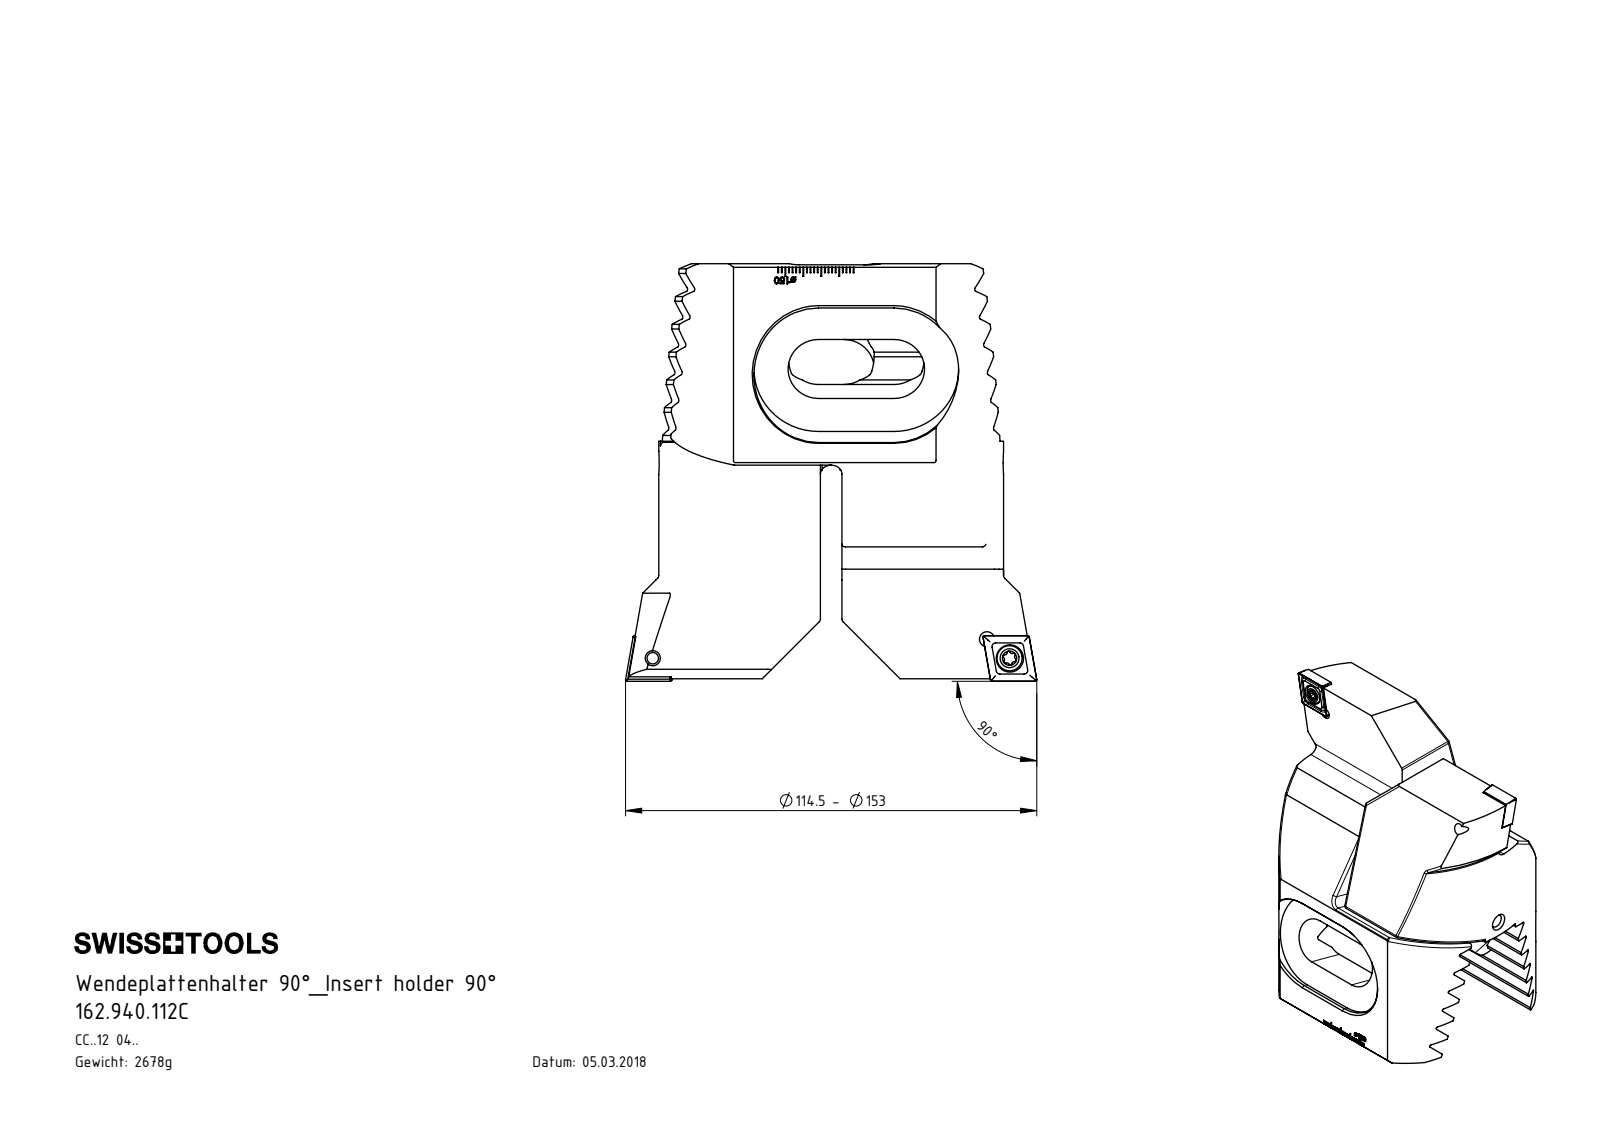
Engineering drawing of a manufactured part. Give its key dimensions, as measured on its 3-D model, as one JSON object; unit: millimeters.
{"part_name": "CCMT120404; WCC-ER2.001.010_A; 162.940.112C; Z94-xxx.001.067_E (+1 more)", "step_written_by": "SolidWorks 2017 (CONFIG_CONTROL_DESIGN)", "units": "millimeters", "bodies": {"solids": 8, "faces": 788, "planar": 448, "cylindrical": 136, "other": 204}, "overall_size": [115.5, 114.5, 75.2], "volume_mm3": 343054, "surface_area_mm2": 64566, "round_holes": [[4.2, 4], [2, 2], [5.5, 2], [7.6, 2], [5, 1]], "round_bosses_or_shafts": [[7, 2], [5, 2], [6, 1], [4, 1]], "partial_cylinders_radius": [[1, 16], [0.39, 12], [0.58, 12], [0.69, 8], [3, 6], [0.69, 4], [8.5, 4], [12, 4]], "face_to_face_distances": [6.93, 20.78, 27.71, 13.85, 13.86, 13.19, 37.3, 37.9, 6.92, 6], "hole_center_spacings": [8.21, 8.33, 25, 93.2, 93.29, 99.43, 48.3, 86.76]}
